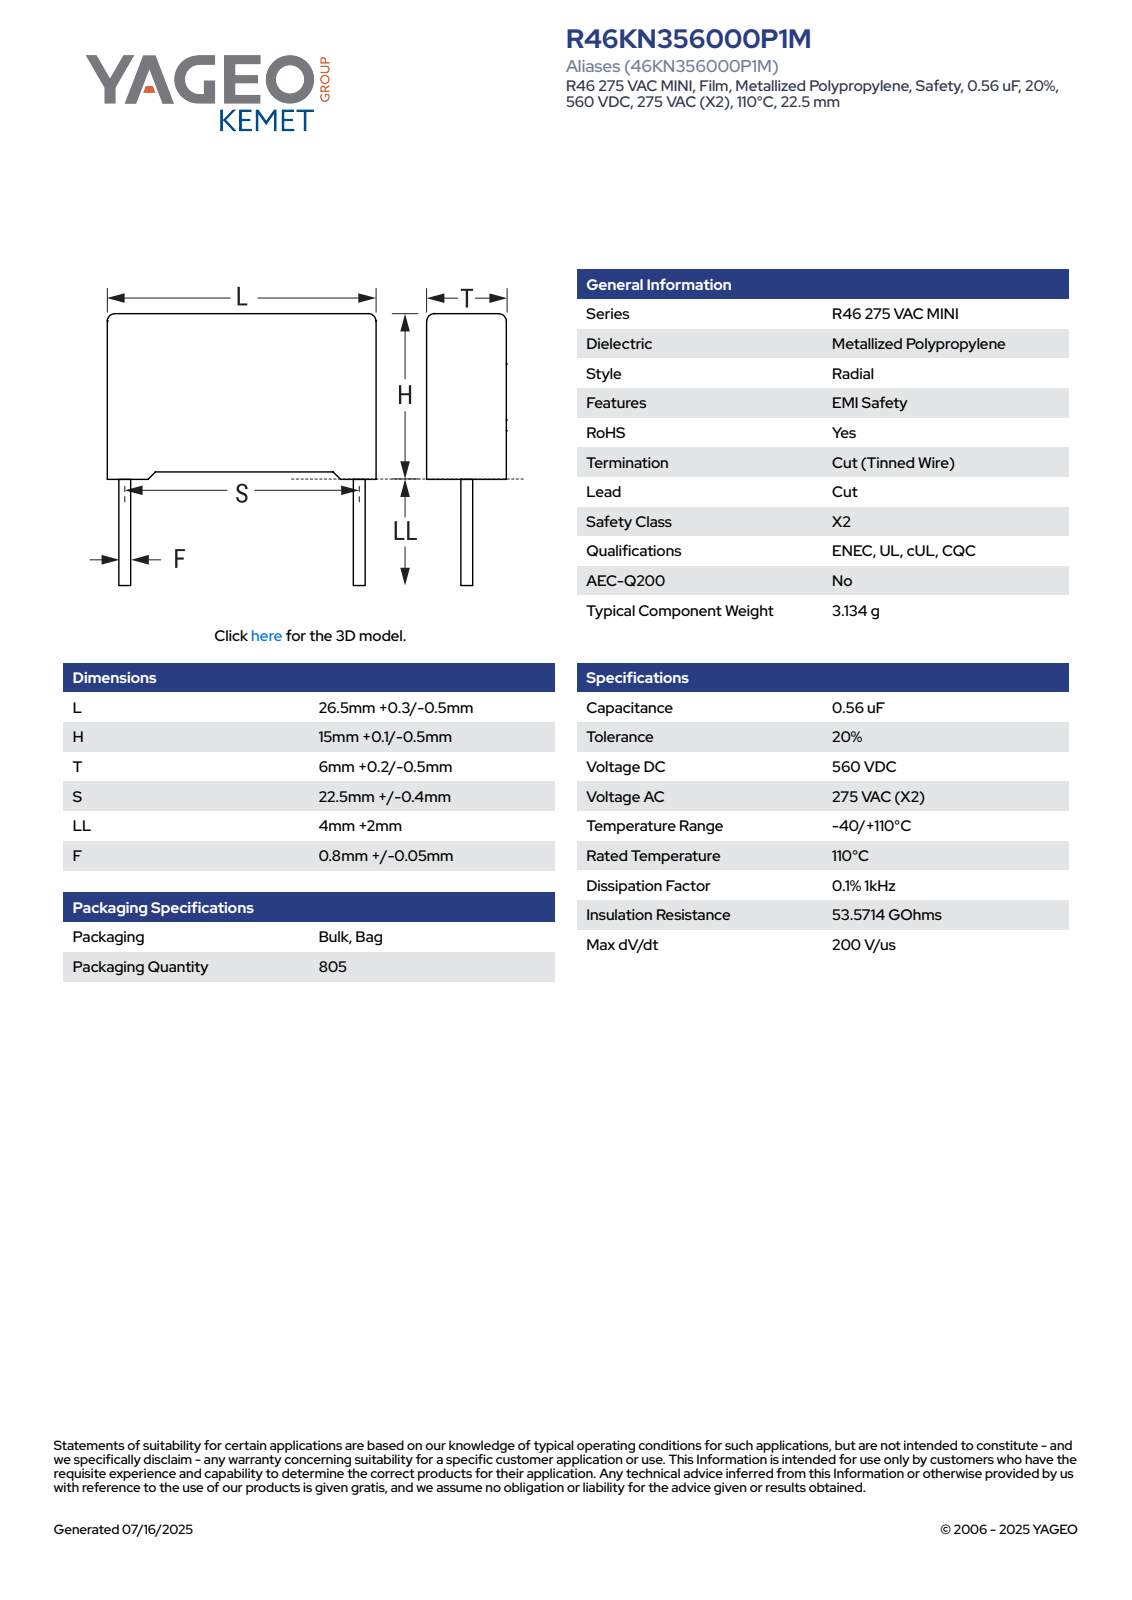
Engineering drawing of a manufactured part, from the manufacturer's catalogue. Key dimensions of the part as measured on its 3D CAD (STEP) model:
Part name (STEP PRODUCT): CFR_RB2_26.5X15X6_L26.8H15.1T6.2S22.5LL6F0.85
STEP written by: SolidWorks 2021 (AUTOMOTIVE_DESIGN)
Units: millimetres
Bodies: 4 solids, 85 faces (77 planar, 8 cylindrical, 0 other)
Overall size (bounding box): 26.8 × 21.1 × 6.21
Volume: 2 413 mm³ · Surface area: 1 410 mm²
Round bosses / shafts (diameter × count): ⌀0.85 ×2
Partial cylindrical surfaces — rounded edges, fillets, slot ends (radius × count): R0.5 ×4
Main face-to-face distances: 6.2, 14.35, 26.8, 14.58, 0.89, 0.52, 0.75, 15.1, 5.31, 4.42
